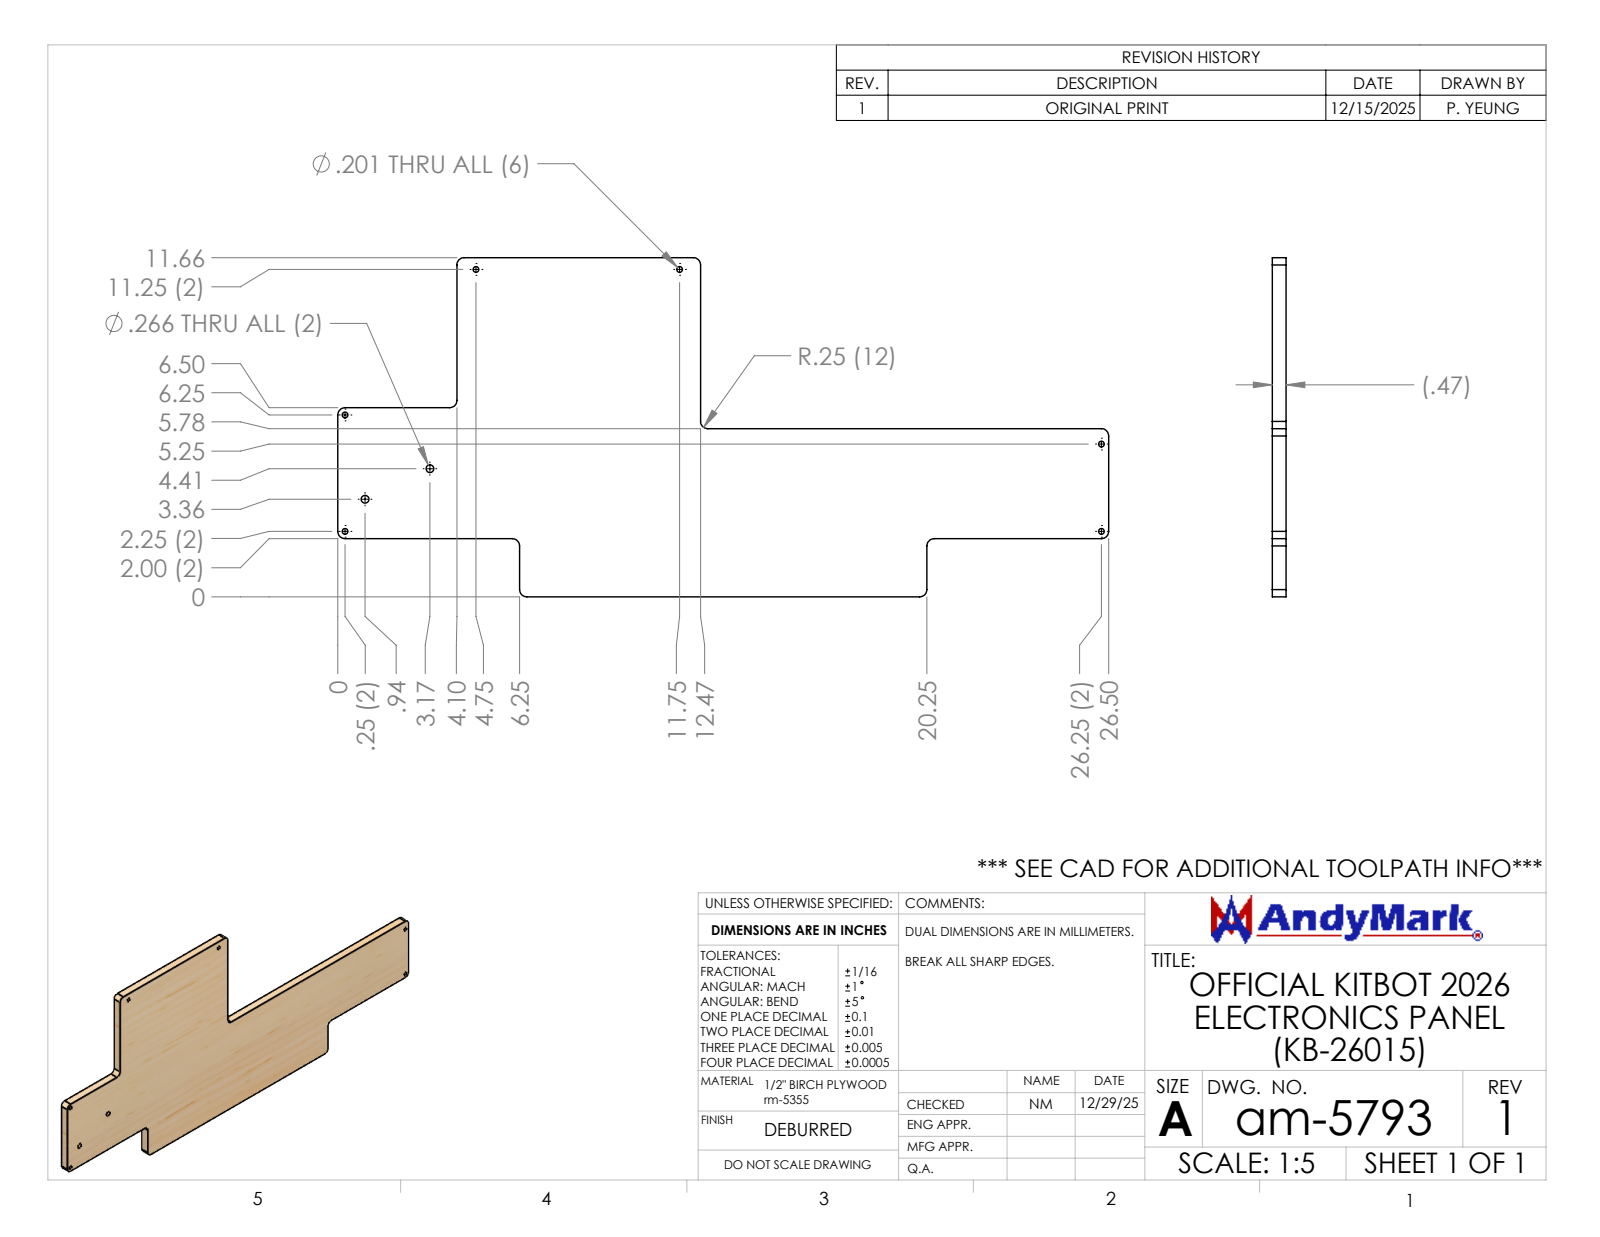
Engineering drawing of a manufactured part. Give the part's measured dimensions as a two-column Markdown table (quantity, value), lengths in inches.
| quantity | value |
| --- | --- |
| part name | am-5793 Electronics Panel (KB-26015) |
| STEP written by | SolidWorks 2024 (AUTOMOTIVE_DESIGN) |
| units | inches |
| bodies | 1 solid, 42 faces (14 planar, 28 cylindrical, 0 other) |
| overall size | 26.5 × 11.655 × 0.469 |
| volume | 84.36 in³ |
| surface area | 397.7 in² |
| round holes (diameter × count) | 0.201 × 6, 0.266 × 2 |
| partial cylindrical surfaces (radius × count) | 0.25 × 12 |
| main face-to-face distances | 0.469, 5.78, 3.78, 2, 5.875, 9.655, 11.655, 8.375, 4.095, 12.47 |
| hole center spacings | 1.302, 2.465, 2.975, 3, 3.452, 3.627, 4, 6.727 |
